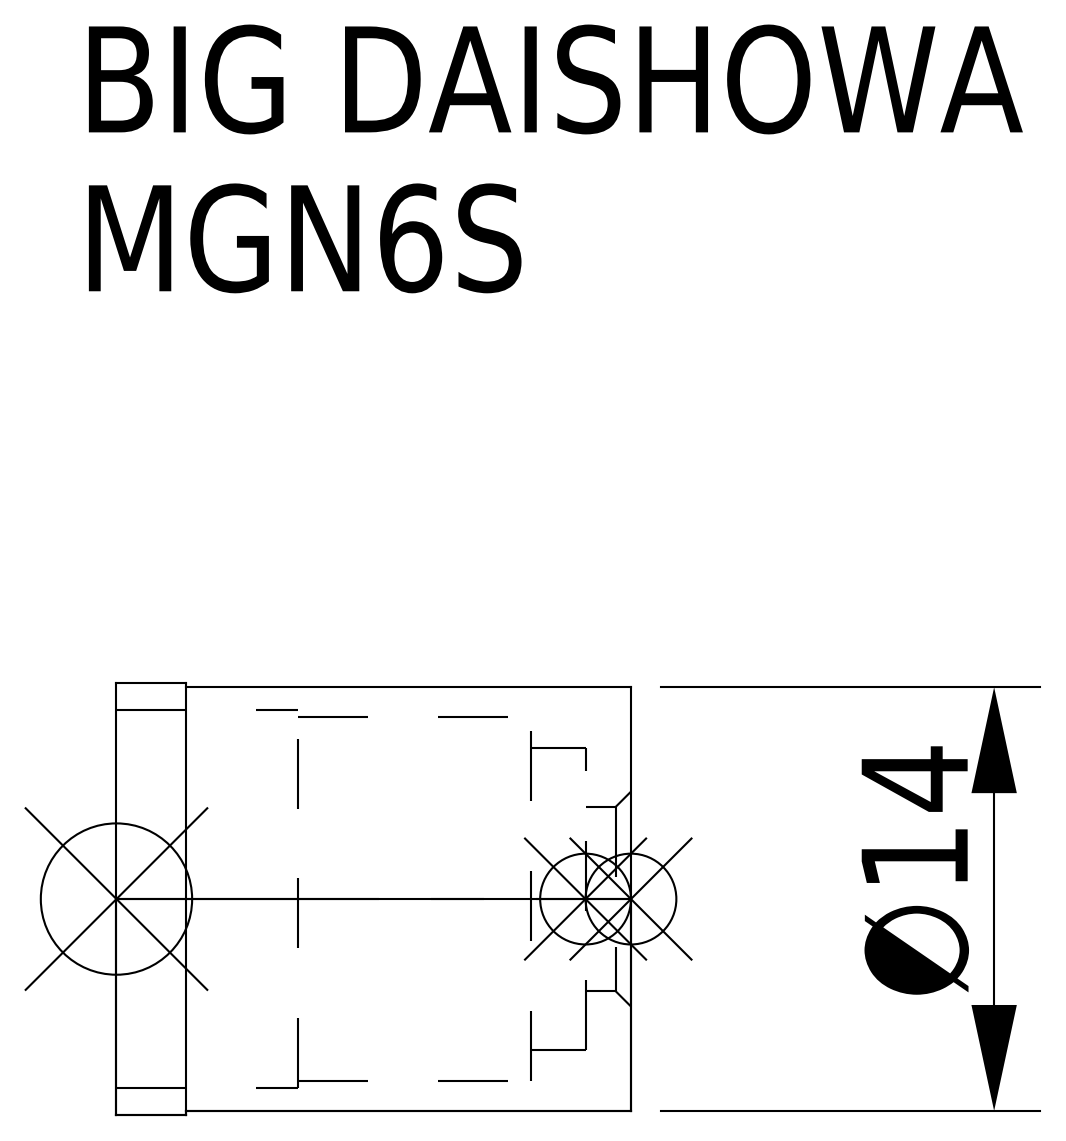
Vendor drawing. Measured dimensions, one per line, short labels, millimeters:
name: MGN6S
written by: CREO PARAMETRIC BY PTC INC, 2016380 (AUTOMOTIVE_DESIGN)
unit: mm
bodies: 1 solid, 20 faces (6 planar, 12 cylindrical, 2 other)
size: 17 × 14.3 × 14.3
volume: 837 mm³; area: 1 619 mm²
holes: 1× ⌀6.1, 1× ⌀10, 1× ⌀12, 1× ⌀12.5
bosses: 1× ⌀14.3, 1× ⌀14
face distances: 1.5, 17, 15.5, 3.3, 1.8, 13.7, 11, 9.5, 7.7, 6
